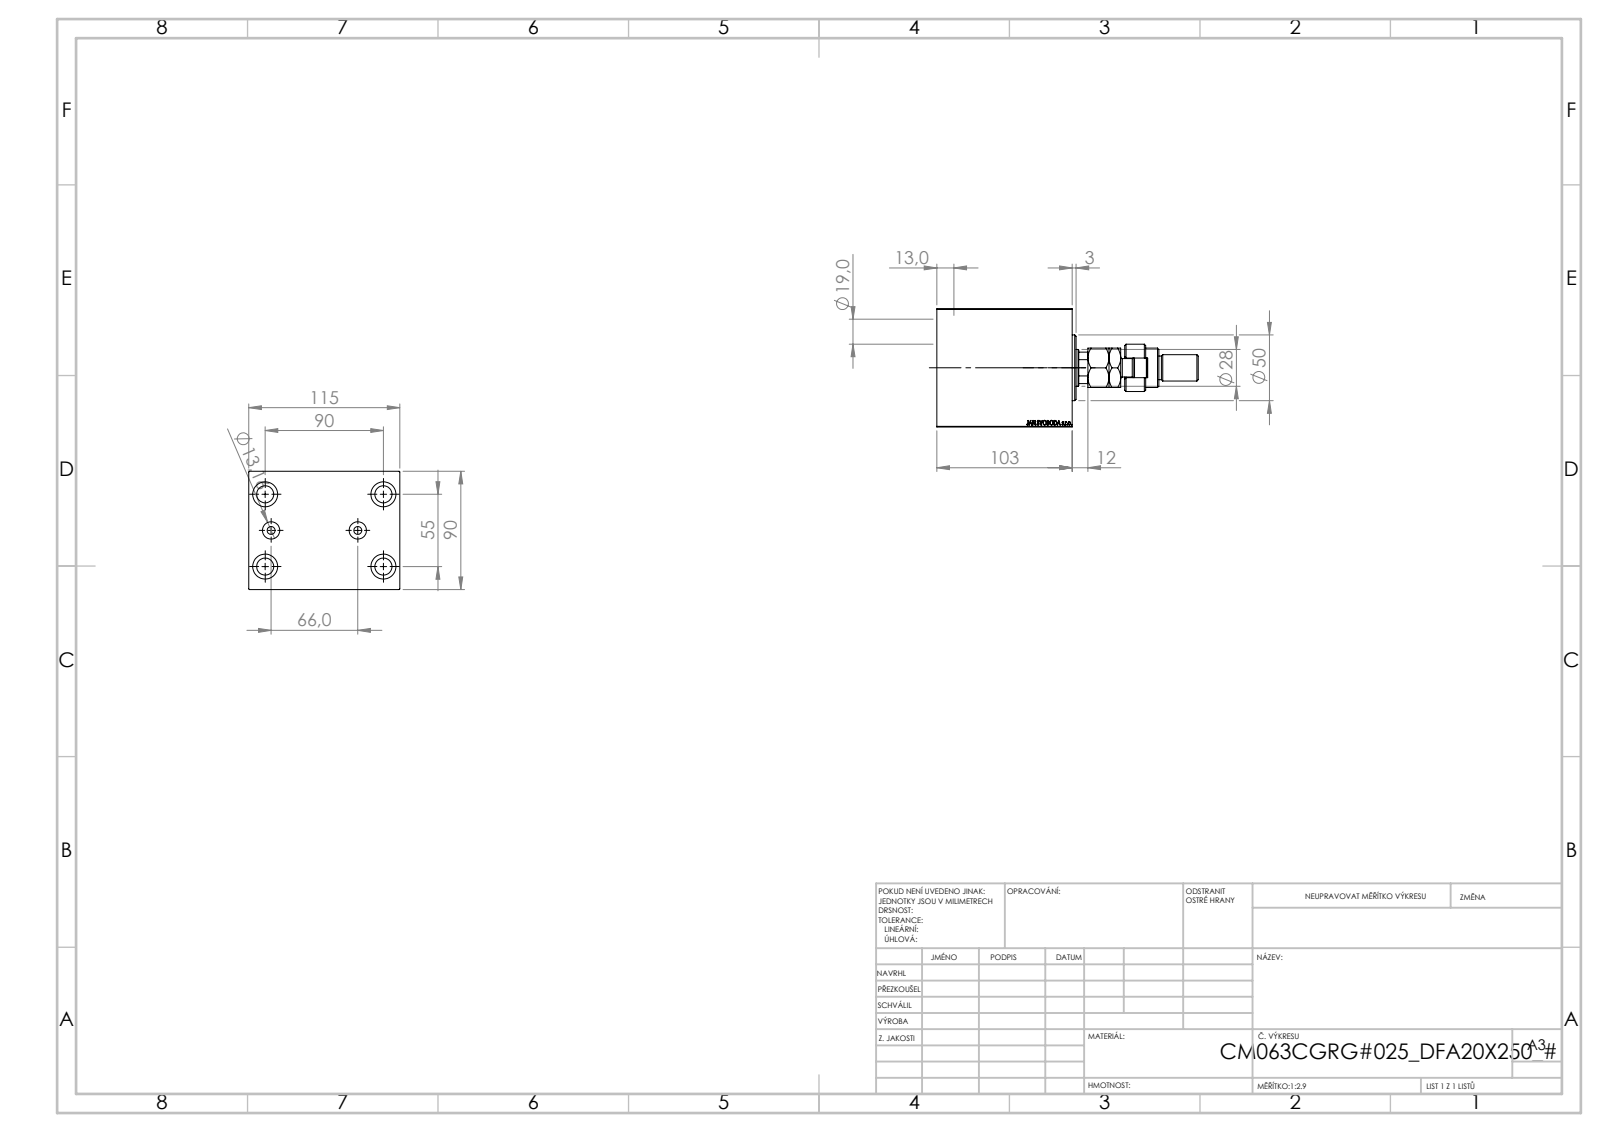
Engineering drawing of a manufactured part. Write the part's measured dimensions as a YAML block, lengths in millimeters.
part_name: "V450CM_C_Body; V450CM_VC_B; MFA; FEMALE_PART_FOR_DFA (+1 more)"
step_written_by: "SolidWorks 2019 (CONFIG_CONTROL_DESIGN)"
units: millimeters
bodies: {solids: 5, faces: 946, planar: 437, cylindrical: 71, other: 438}
overall_size: [200.5, 115, 90]
volume: 978897
surface_area: 133571
round_holes:
  - {diameter: 13, count: 4}
  - {diameter: 19, count: 4}
  - {diameter: 6, count: 2}
  - {diameter: 13.16, count: 2}
  - {diameter: 18.5, count: 1}
  - {diameter: 28, count: 1}
  - {diameter: 31.5, count: 1}
  - {diameter: 63, count: 1}
  - {diameter: 65, count: 1}
  - {diameter: 72, count: 1}
round_bosses_or_shafts:
  - {diameter: 50, count: 1}
  - {diameter: 36, count: 1}
  - {diameter: 30, count: 1}
  - {diameter: 22, count: 1}
  - {diameter: 20, count: 1}
  - {diameter: 18, count: 1}
  - {diameter: 14, count: 1}
partial_cylinders:
  - {radius: 7.5, count: 1}
  - {radius: 12, count: 1}
  - {radius: 13.5, count: 1}
face_to_face_distances: [90, 115, 103, 53.25, 49.75, 10, 93, 30, 25, 5]
hole_center_spacings: [30, 52.74, 82.71, 33, 55, 90, 105.48, 66]
